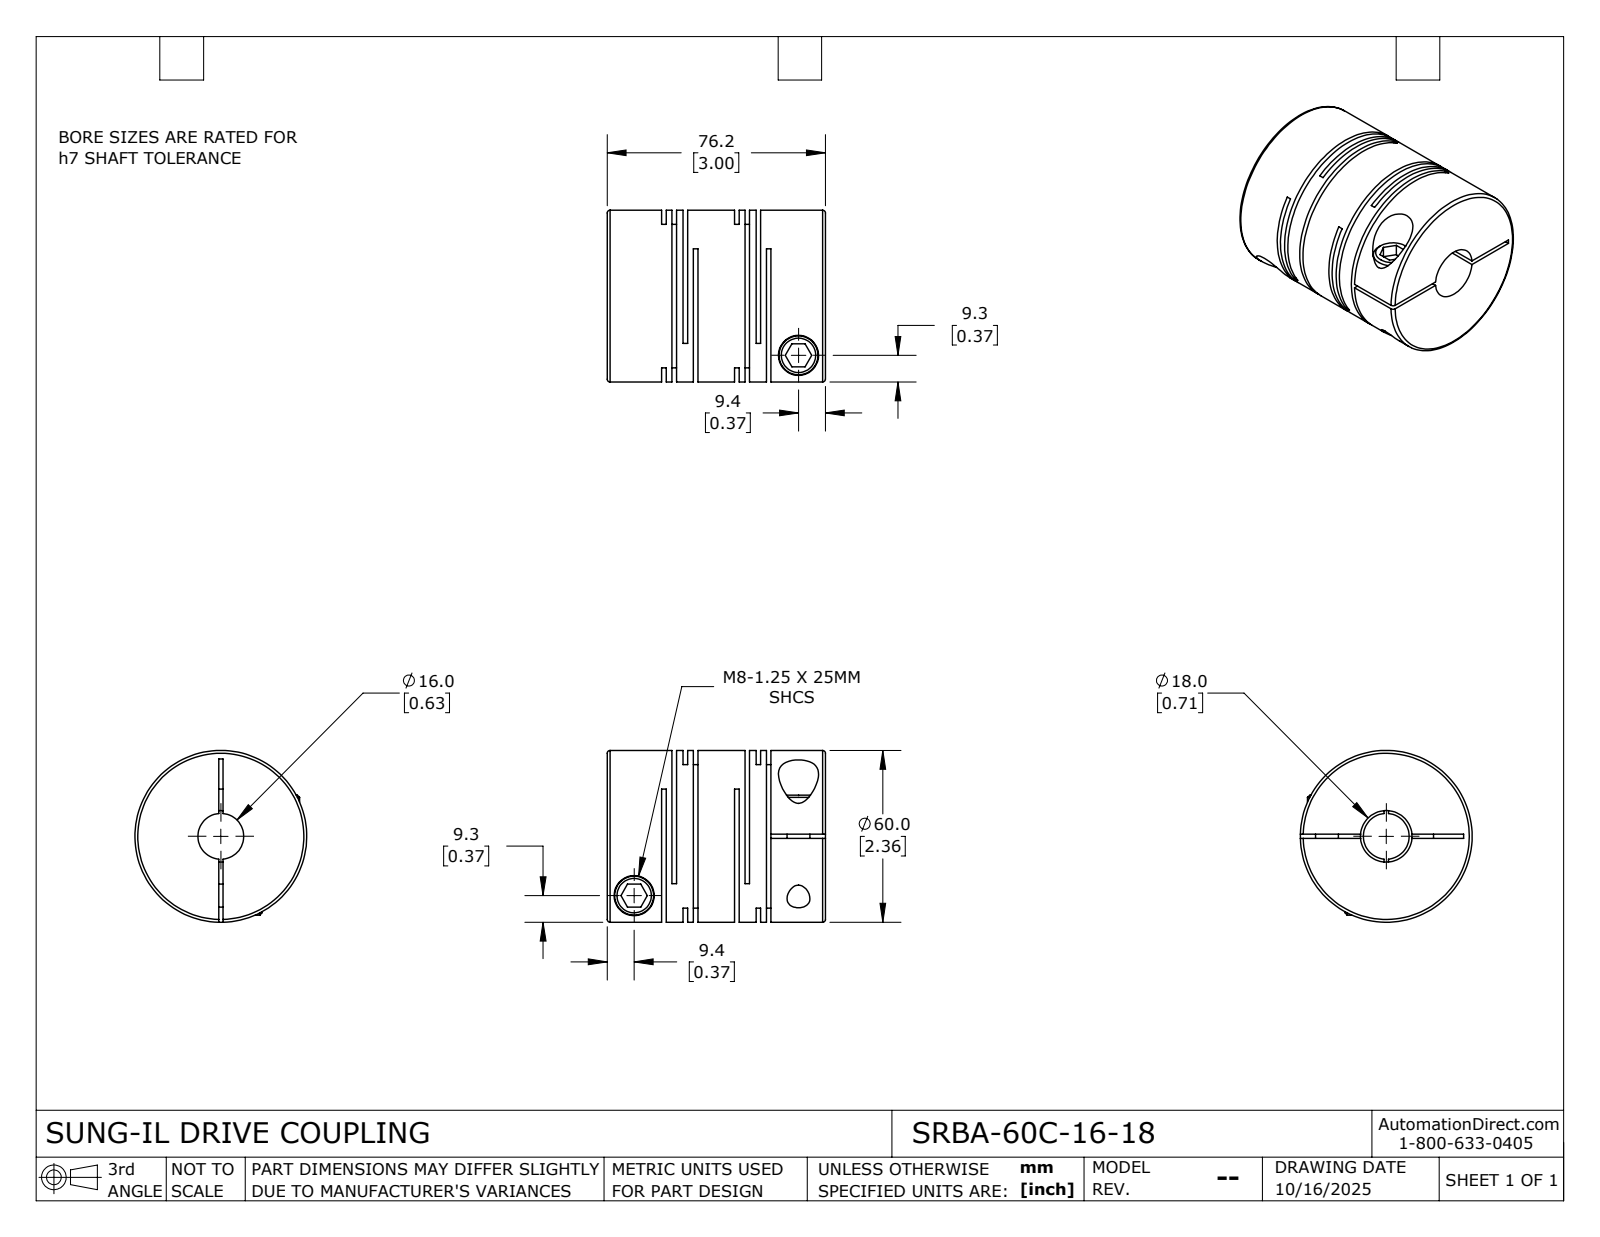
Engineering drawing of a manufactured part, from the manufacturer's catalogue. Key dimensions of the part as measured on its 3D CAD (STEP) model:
Part name (STEP PRODUCT): SRBA-60C-16-18
STEP written by: SolidWorks 2024 (CONFIG_CONTROL_DESIGN)
Units: millimetres
Bodies: 1 solid, 115 faces (60 planar, 42 cylindrical, 13 other)
Overall size (bounding box): 76.2 × 60 × 60
Volume: 164 906 mm³ · Surface area: 59 995 mm²
Round holes (diameter × count): ⌀8 ×2, ⌀14 ×2, ⌀16 ×1, ⌀18 ×1
Round bosses / shafts (diameter × count): ⌀13.6 ×2, ⌀60 ×1
Main face-to-face distances: 1.6, 25.5, 7.5, 3.6, 33, 2, 5.9, 23.9, 3.9, 21.9
